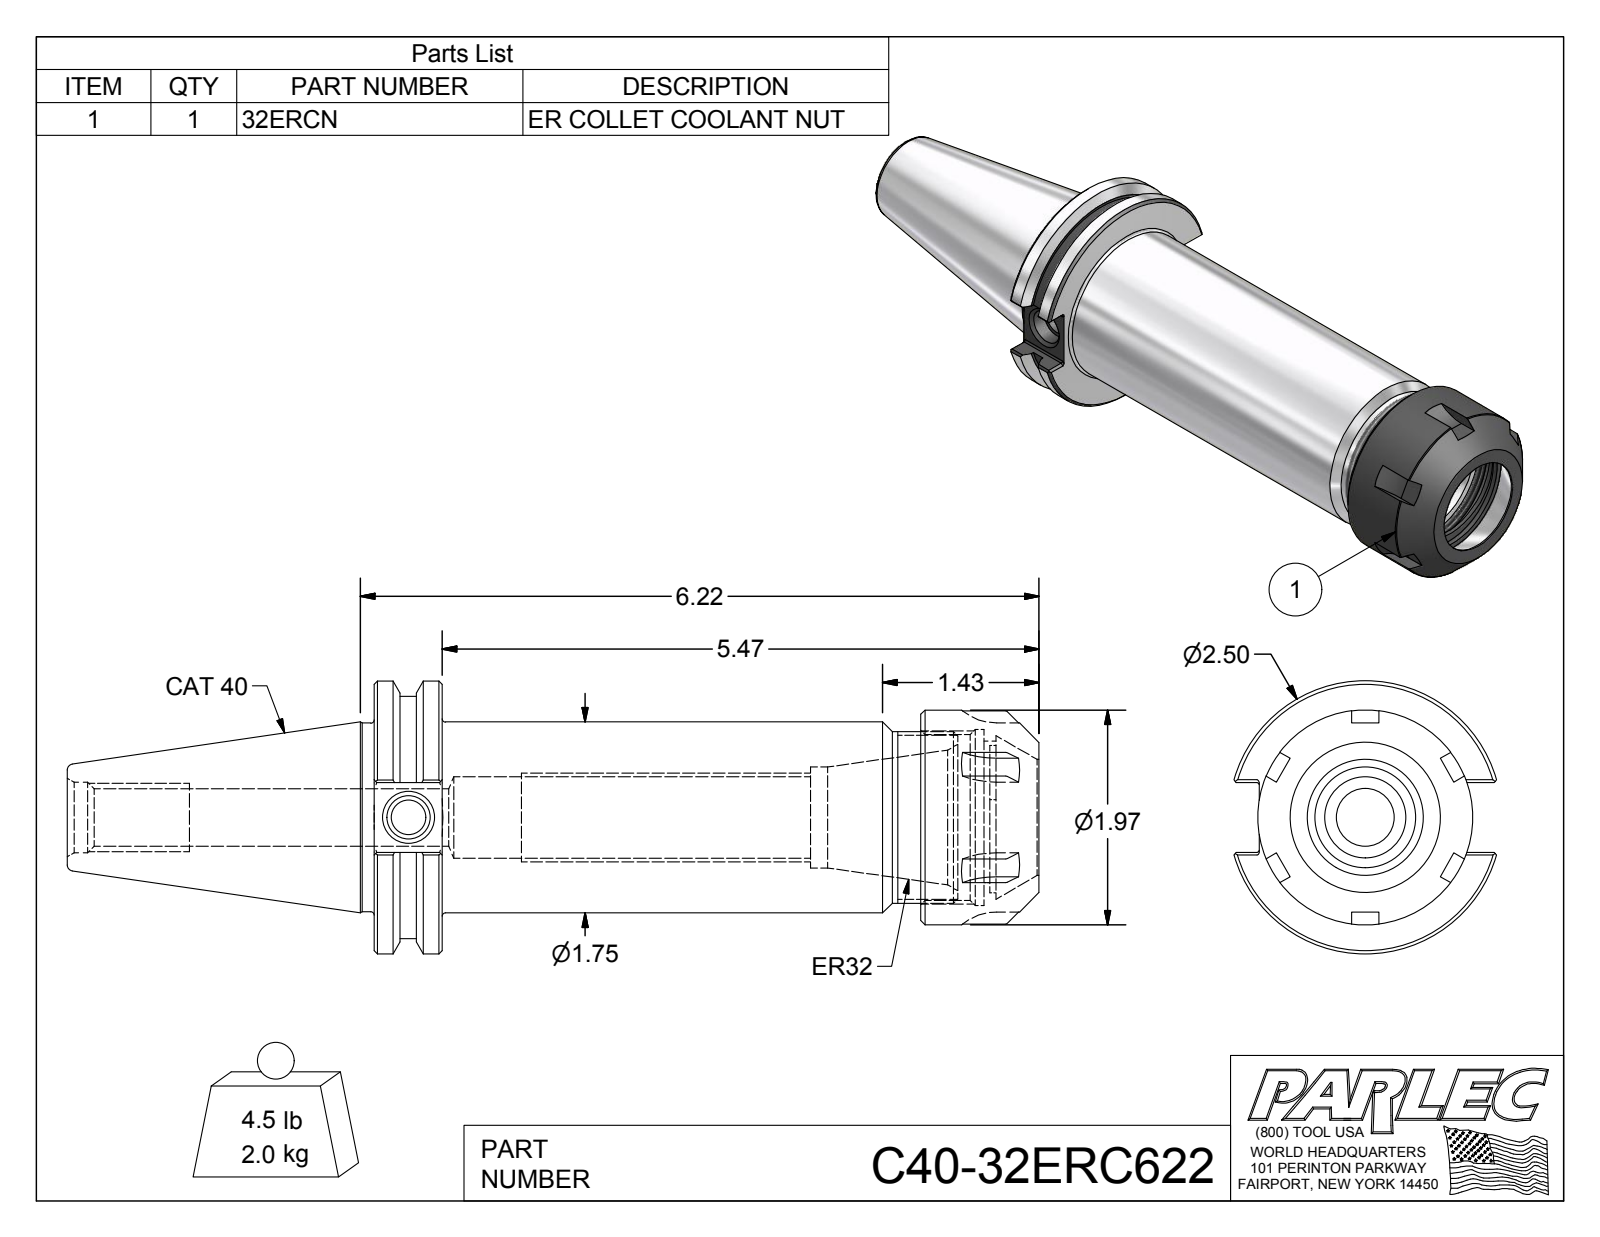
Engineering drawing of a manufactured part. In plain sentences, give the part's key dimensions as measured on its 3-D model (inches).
The part is named "C40-32ERC622; C40-32ER6-1; 32ERCN". Its 3-D file was written by "Autodesk Inventor 2012 (AUTOMOTIVE_DESIGN)". It is 2 solids with 127 faces: 55 planar, 39 cylindrical and 33 other. Overall it measures 8.908 by 2.5 by 2.403 inches. Its volume is 15.74 cubic inches and its surface area 83.54 square inches. Round holes: 1 of diameter 0.315, 1 of diameter 0.399, 1 of diameter 0.527, 1 of diameter 0.648, 1 of diameter 0.745, 1 of diameter 0.925, 1 of diameter 1.063, 1 of diameter 1.299, 1 of diameter 1.522, 1 of diameter 1.614. Round bosses or shafts: 1 of diameter 2.5, 1 of diameter 2.219, 1 of diameter 1.969, 1 of diameter 1.75, 1 of diameter 1.73, 1 of diameter 1.575. Partial cylindrical surfaces (rounded edges, fillets, slot ends): 12 of radius 0.02, 6 of radius 0.5, 1 of radius 0.689. The main face-to-face distances are 0.625, 5.012, 4.387, 5.591, 4.966, 0.579, 6.095, 5.47, 1.083, 0.504. The hole center spacings are 0.059.
